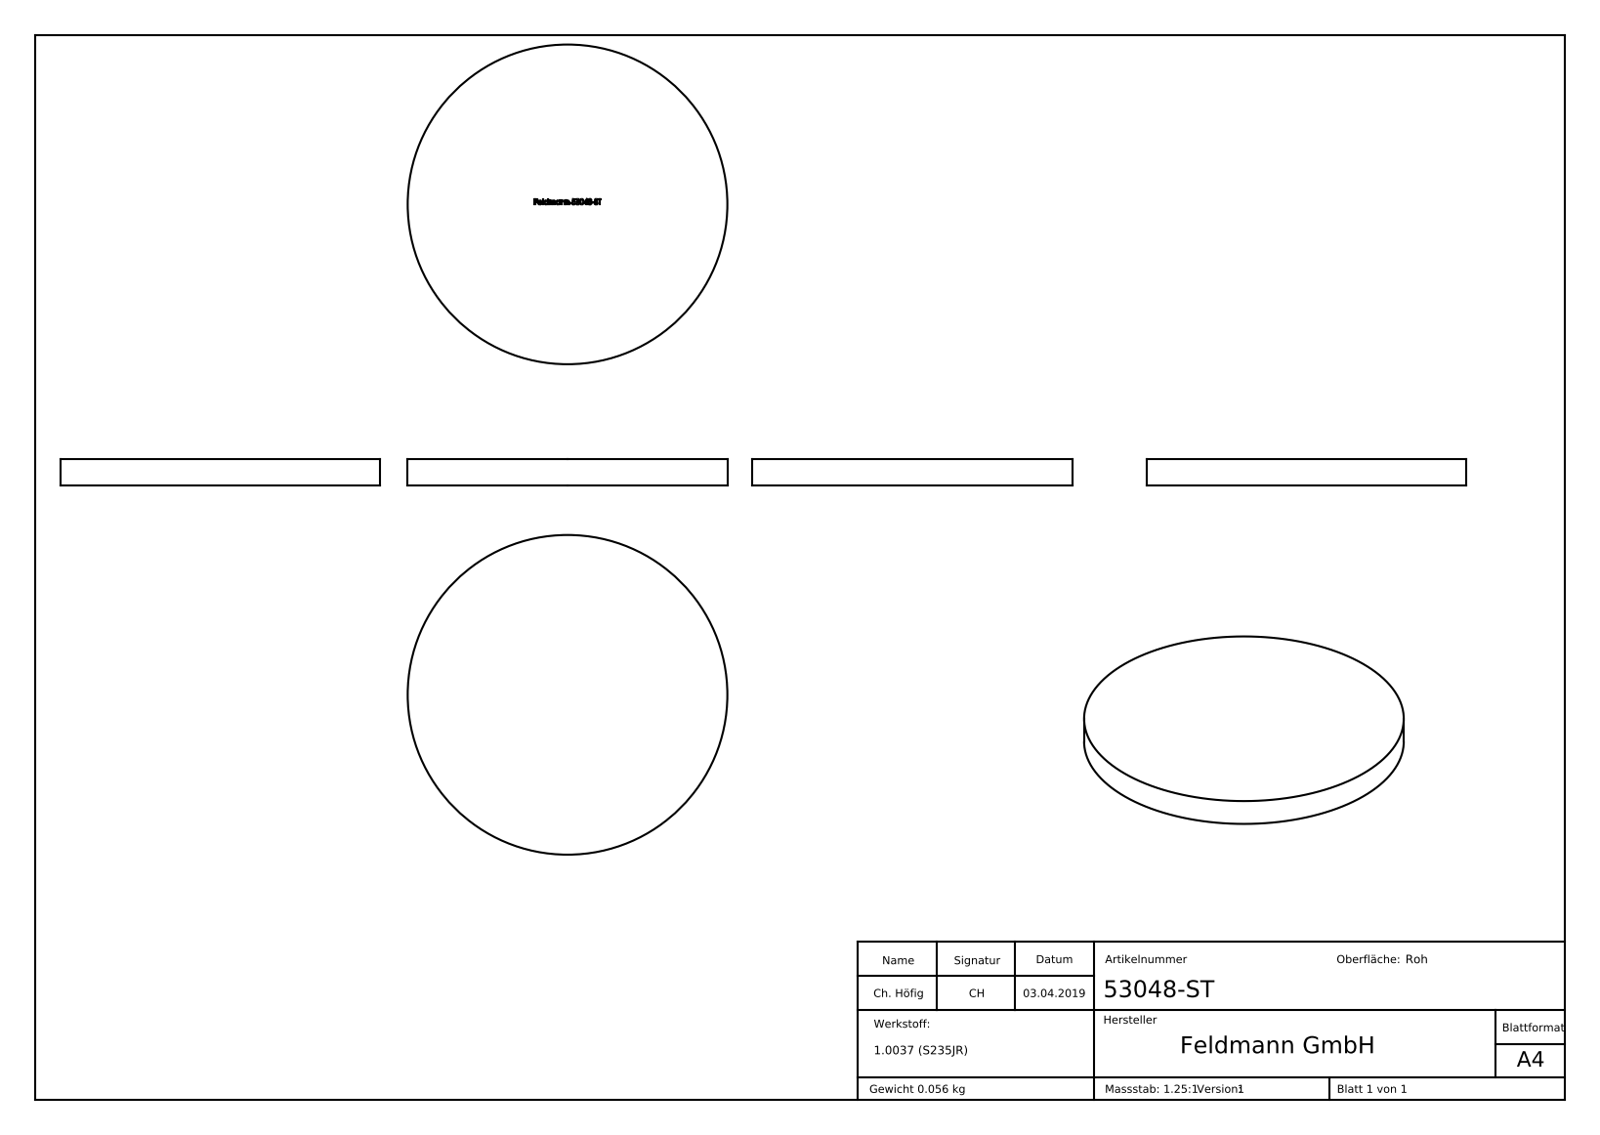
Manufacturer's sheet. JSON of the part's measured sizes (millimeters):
{"part_name": "53048-ST", "step_written_by": "SolidWorks 2015 (CONFIG_CONTROL_DESIGN)", "units": "millimeters", "bodies": {"solids": 1, "faces": 228, "planar": 115, "cylindrical": 2, "other": 111}, "overall_size": [48, 48, 4], "volume_mm3": 7238, "surface_area_mm2": 4228, "round_bosses_or_shafts": [[48, 1]], "face_to_face_distances": [4, 3.9, 0.44, 0.79, 0.99, 1.78, 1.21, 8.49, 9.7, 0.75]}
